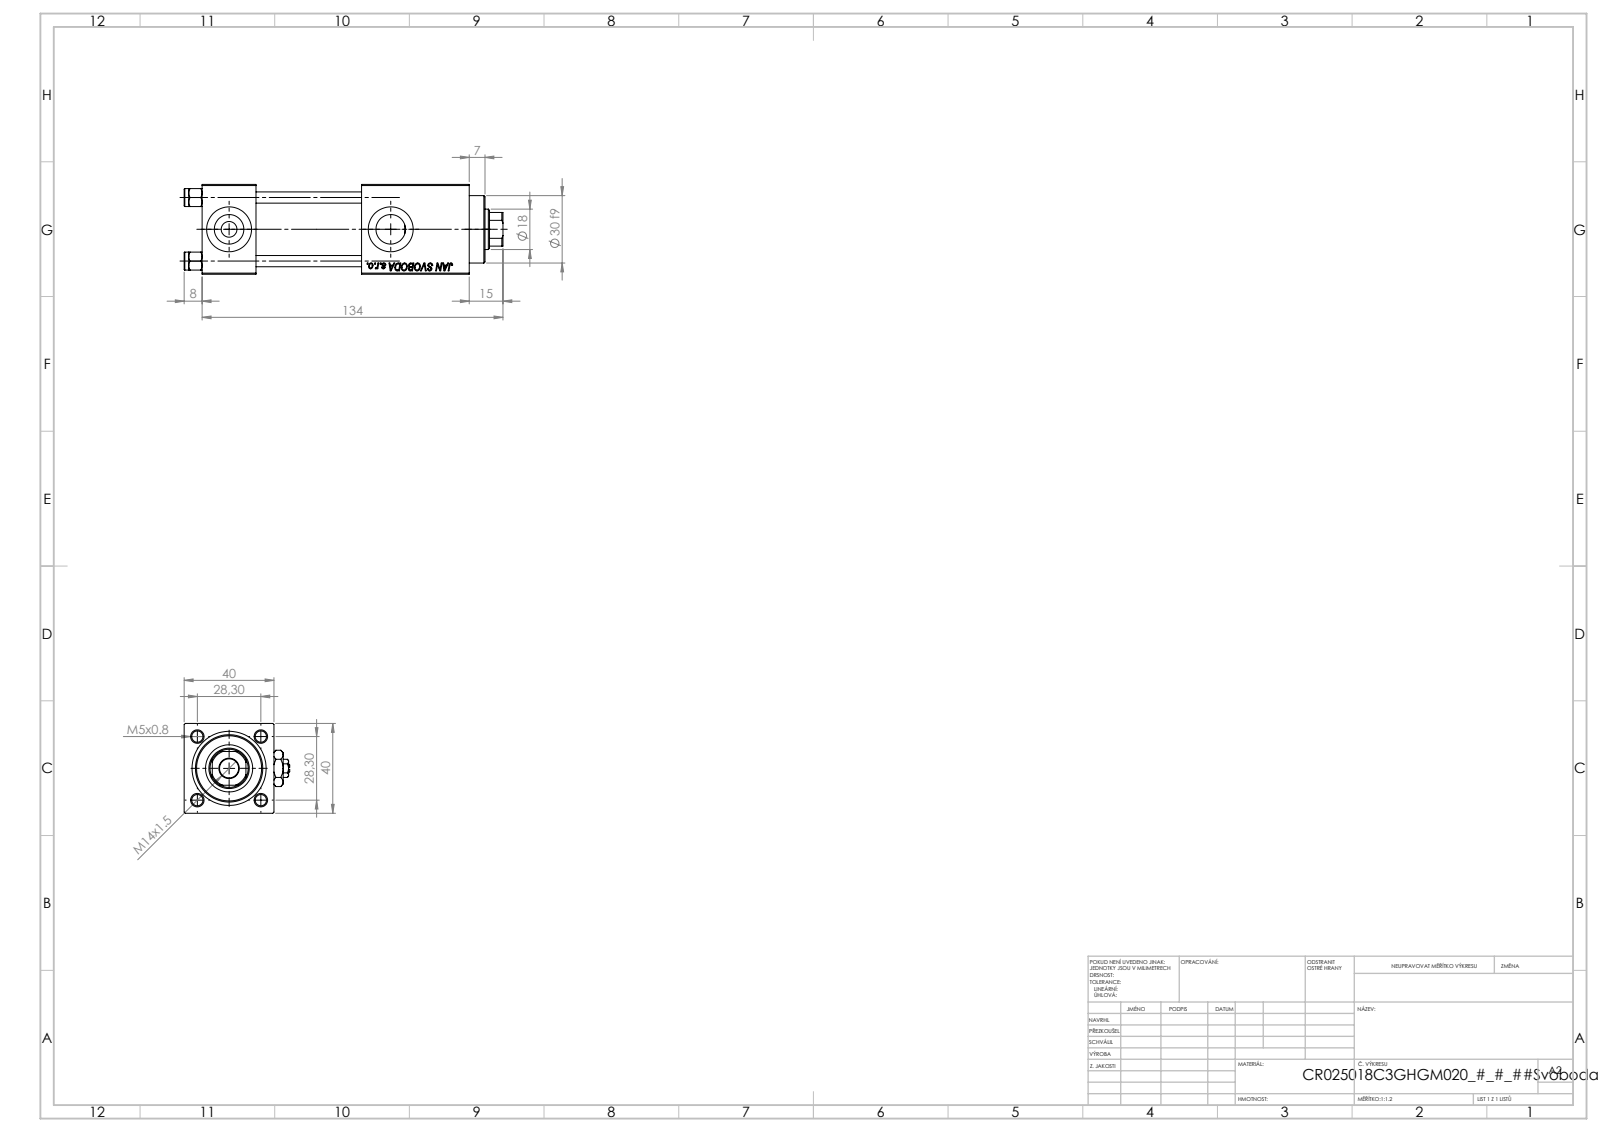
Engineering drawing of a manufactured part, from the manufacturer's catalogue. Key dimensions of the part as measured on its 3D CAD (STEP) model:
Part name (STEP PRODUCT): Zatka_pro_OIL_PORT; V215CR_C_TYCINKA; V215_VC_A; NUT_M5_C (+2 more)
STEP written by: SolidWorks 2019 (CONFIG_CONTROL_DESIGN)
Units: millimetres
Bodies: 13 solids, 1245 faces (571 planar, 96 cylindrical, 578 other)
Overall size (bounding box): 142 × 47 × 40
Volume: 148 592 mm³ · Surface area: 58 485 mm²
Round holes (diameter × count): ⌀5 ×4, ⌀20 ×3, ⌀7 ×2, ⌀13.16 ×2, ⌀8.5 ×1, ⌀18 ×1, ⌀21 ×1, ⌀25 ×1, ⌀30 ×1
Round bosses / shafts (diameter × count): ⌀8 ×4, ⌀31 ×1
Partial cylindrical surfaces — rounded edges, fillets, slot ends (radius × count): R8.5 ×1
Main face-to-face distances: 40, 24, 39.8, 47, 71, 90.3, 66.3, 19.3, 48, 119
Hole centre spacings: 20.01, 28.3, 40.02, 72
